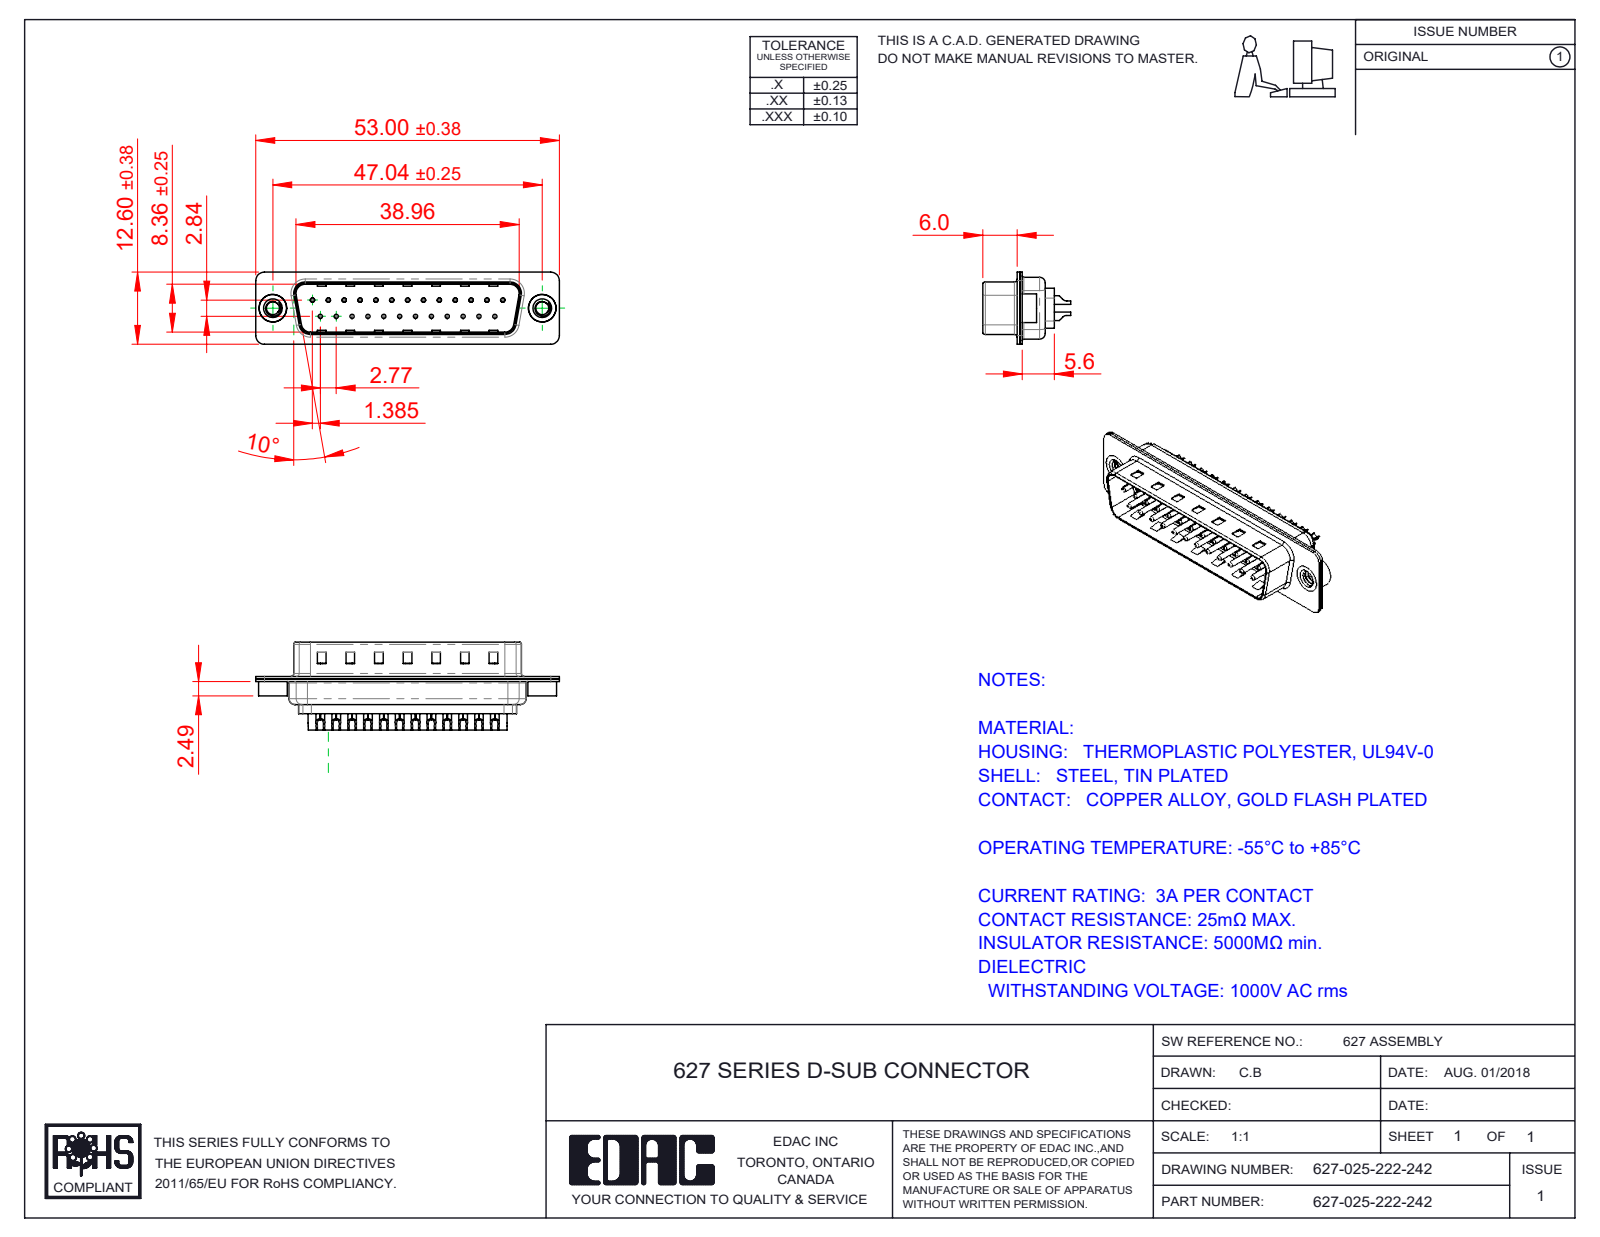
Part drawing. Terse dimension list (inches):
name: 627 Shell Rear_25 Contacts; 627-025-222-042; 627 4-40 Threaded Rivet; 627 Shell Front_25 Contacts (+3 more)
written by: SolidWorks 2020 (CONFIG_CONTROL_DESIGN)
unit: in
bodies: 30 solids, 1972 faces (521 planar, 860 cylindrical, 591 other)
size: 2.087 × 0.604 × 0.496
volume: 0.164 in³; area: 12.16 in²
holes: 25× ⌀0.014, 25× ⌀0.043, 25× ⌀0.063, 2× ⌀0.089, 2× ⌀0.157, 2× ⌀0.189
bosses: 25× ⌀0.079, 25× ⌀0.059, 25× ⌀0.03, 2× ⌀0.197, 2× ⌀0.193
rounds: 16× R0.059, 12× R0.079, 8× R0.02, 8× R0.063, 6× R0.039, 4× R0.01, 4× R0.024, 4× R0.026
face distances: 0.016, 0.018, 0.032, 0.377, 0.345, 0.035, 0.059, 0.055, 0.256, 0.238
hole spacings: 0.124, 0.327, 0.109, 0.218, 0.436, 0.654, 0.198, 0.198
